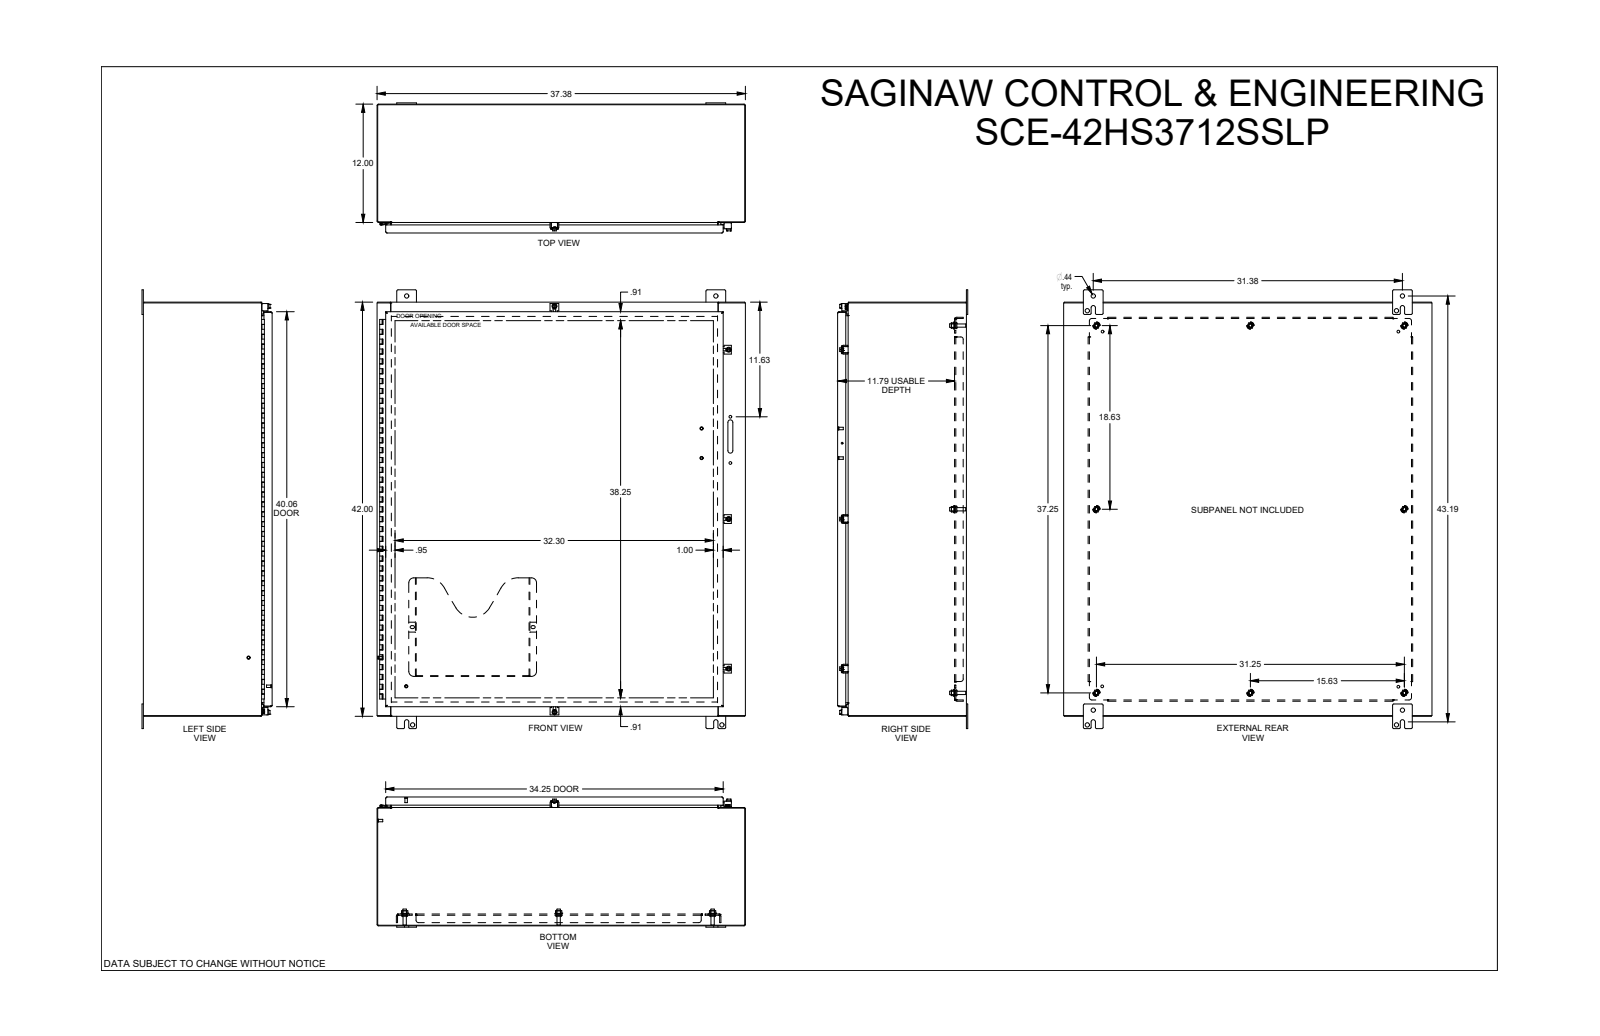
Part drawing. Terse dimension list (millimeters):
name: SCE-42HS3712LP
written by: SolidWorks 2021 (AUTOMOTIVE_DESIGN)
unit: mm
bodies: 83 solids, 3710 faces (1424 planar, 1110 cylindrical, 1176 other)
size: 1130.3 × 949.3 × 338.9
volume: 10 130 000 mm³; area: 9 150 000 mm²
holes: 8× ⌀9.3, 8× ⌀12.7, 6× ⌀4.4, 6× ⌀5.2, 6× ⌀6.2, 6× ⌀7.1, 6× ⌀9.5, 5× ⌀5.2, 4× ⌀7.9, 4× ⌀7.9, 3× ⌀1, 3× ⌀5.5
bosses: 11× ⌀6.4, 11× ⌀6.3, 9× ⌀4.3, 8× ⌀9.3, 8× ⌀8.4, 6× ⌀6.1, 5× ⌀12.9, 4× ⌀15
rounds: 217× R0.3, 92× R0.6, 28× R0.4, 21× R4.7, 20× R1, 16× R1.5, 16× R1.5, 12× R0.7
face distances: 1.9, 330, 328.1, 331.9, 28.6, 30.5, 301.4, 299.5, 3.2, 302.7
hole spacings: 412.8, 22.2, 381.5, 412.8, 425.2, 457.6, 617.5, 793.8
